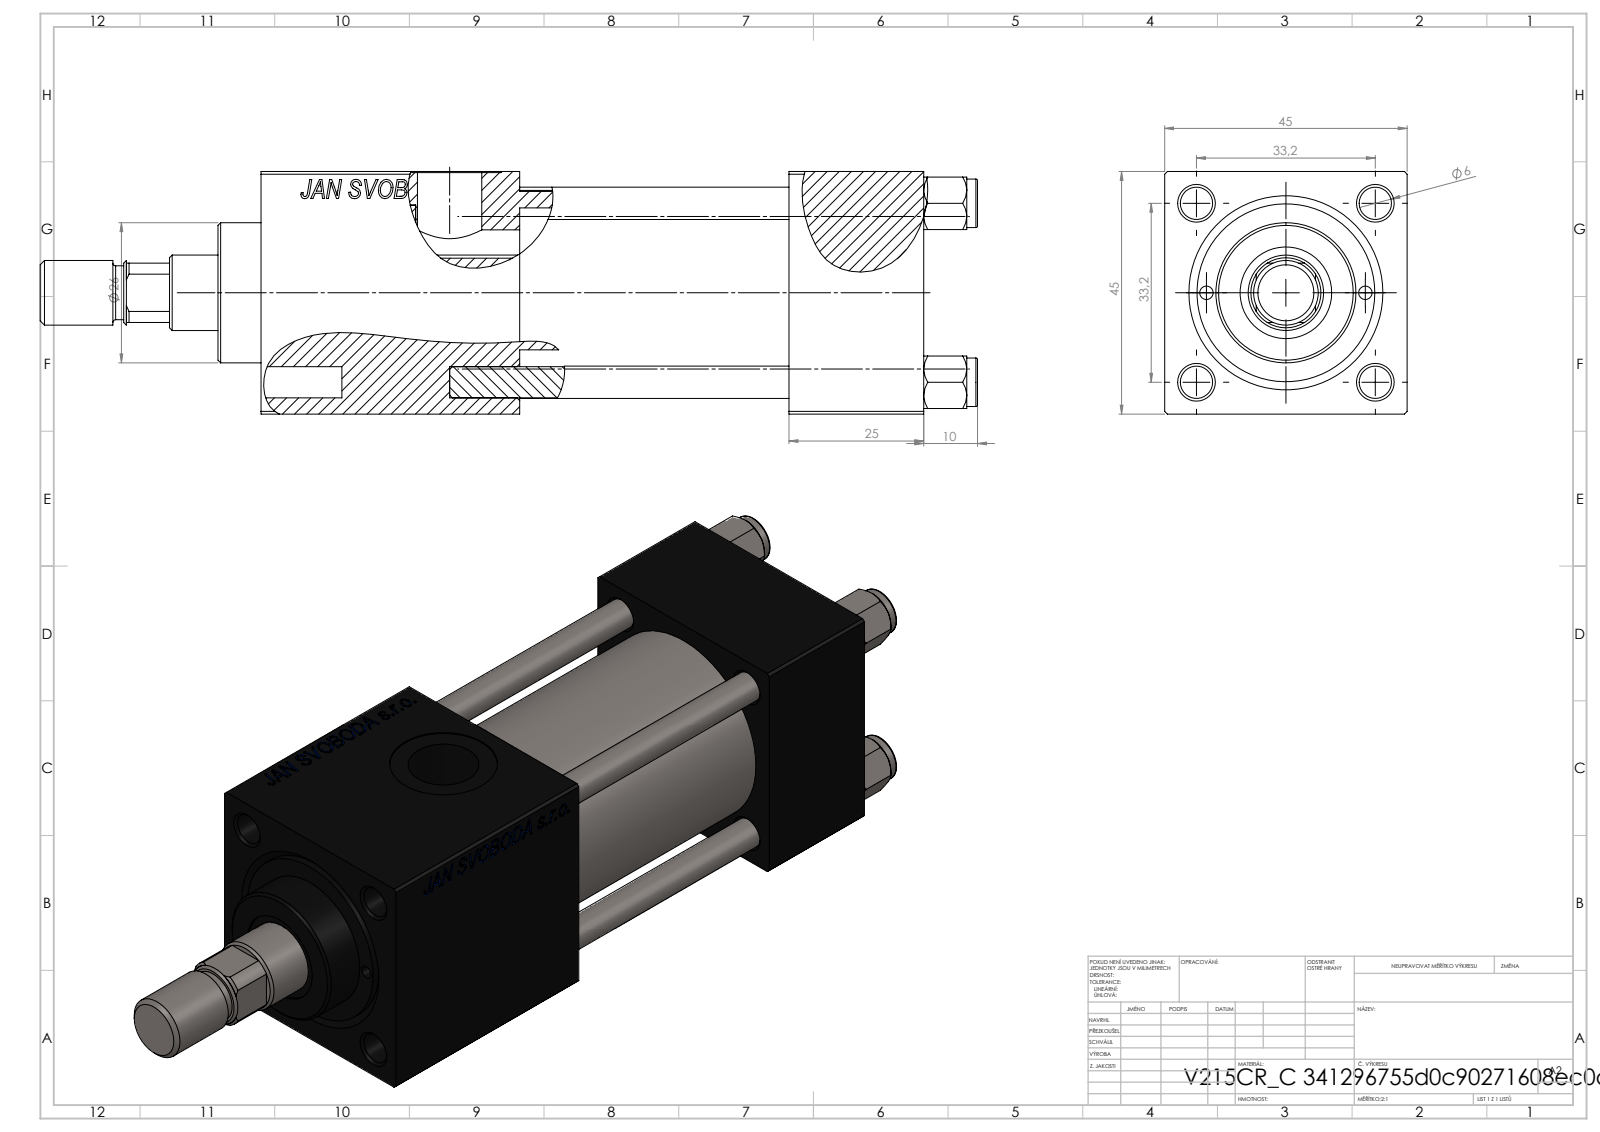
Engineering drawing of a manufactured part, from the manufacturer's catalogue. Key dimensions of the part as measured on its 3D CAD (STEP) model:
Part name (STEP PRODUCT): V215CR_VCP_C; ROD_END_AH; V215CR_C_Body; NUT_M5_C (+2 more)
STEP written by: SolidWorks 2019 (CONFIG_CONTROL_DESIGN)
Units: millimetres
Bodies: 12 solids, 1168 faces (531 planar, 95 cylindrical, 542 other)
Overall size (bounding box): 174 × 45 × 45
Volume: 195 503 mm³ · Surface area: 68 012 mm²
Round holes (diameter × count): ⌀6 ×4, ⌀2.5 ×2, ⌀7 ×2, ⌀13.16 ×2, ⌀20 ×2, ⌀6.5 ×1, ⌀14 ×1, ⌀17 ×1, ⌀24 ×1, ⌀32 ×1, ⌀33 ×1
Round bosses / shafts (diameter × count): ⌀9 ×4, ⌀38 ×1, ⌀26 ×1, ⌀12 ×1, ⌀10 ×1
Partial cylindrical surfaces — rounded edges, fillets, slot ends (radius × count): R6.5 ×1
Main face-to-face distances: 45, 25, 123, 98, 50, 75, 48, 94.3, 69.3, 19.3
Hole centre spacings: 16.7, 23.48, 33.2, 35.47, 14.75, 46.95, 29.5, 75.5
